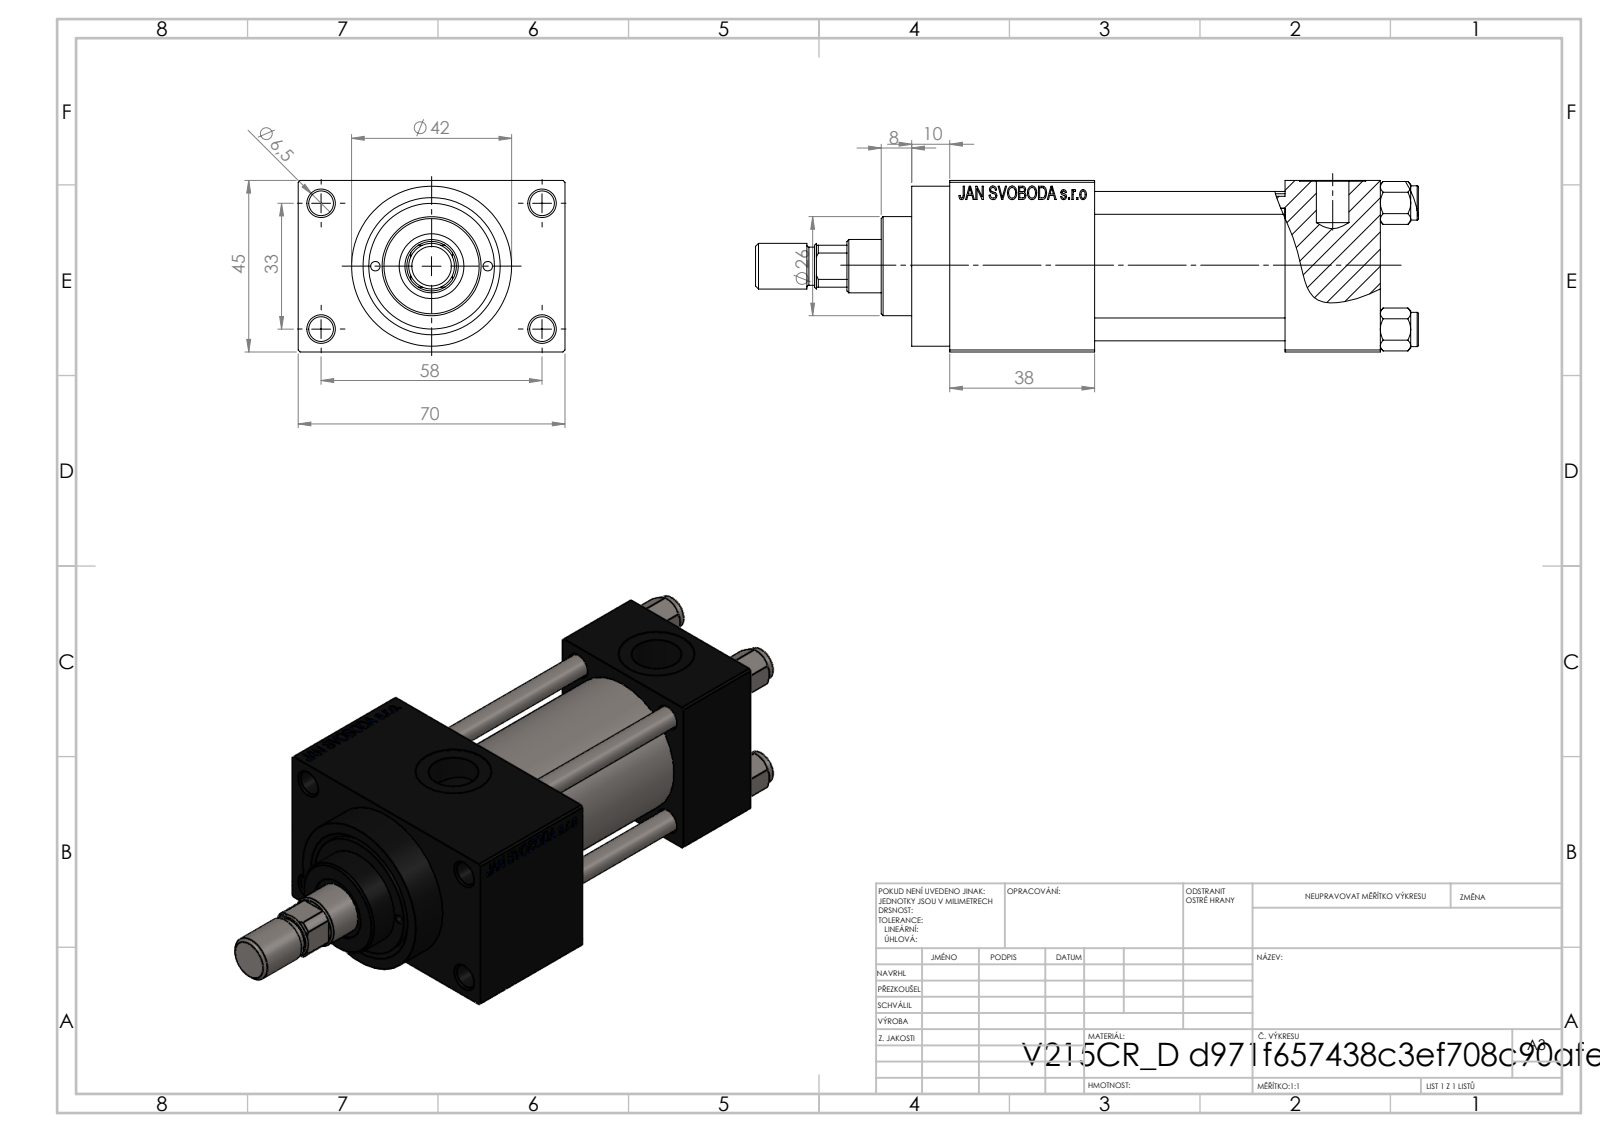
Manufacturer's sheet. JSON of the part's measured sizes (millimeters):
{"part_name": "V215CR_VCP_D; ROD_END_AH; V215_VC_A; NUT_M5_D (+2 more)", "step_written_by": "SolidWorks 2019 (CONFIG_CONTROL_DESIGN)", "units": "millimeters", "bodies": {"solids": 12, "faces": 1125, "planar": 502, "cylindrical": 97, "other": 526}, "overall_size": [174, 70, 45], "volume_mm3": 233504, "surface_area_mm2": 75712, "round_holes": [[6.5, 5], [6, 4], [2.5, 2], [7, 2], [13.16, 2], [20, 2], [14, 1], [17, 1], [24, 1], [32, 1], [33, 1]], "round_bosses_or_shafts": [[9, 4], [42, 1], [38, 1], [26, 1], [12, 1], [10, 1]], "partial_cylinders_radius": [[6.5, 1]], "face_to_face_distances": [45, 25, 12.5, 57.5, 50, 75, 88, 70, 38, 113], "hole_center_spacings": [12.4, 16.7, 21.8, 23.48, 33.2, 33.37, 35.35, 35.47]}
